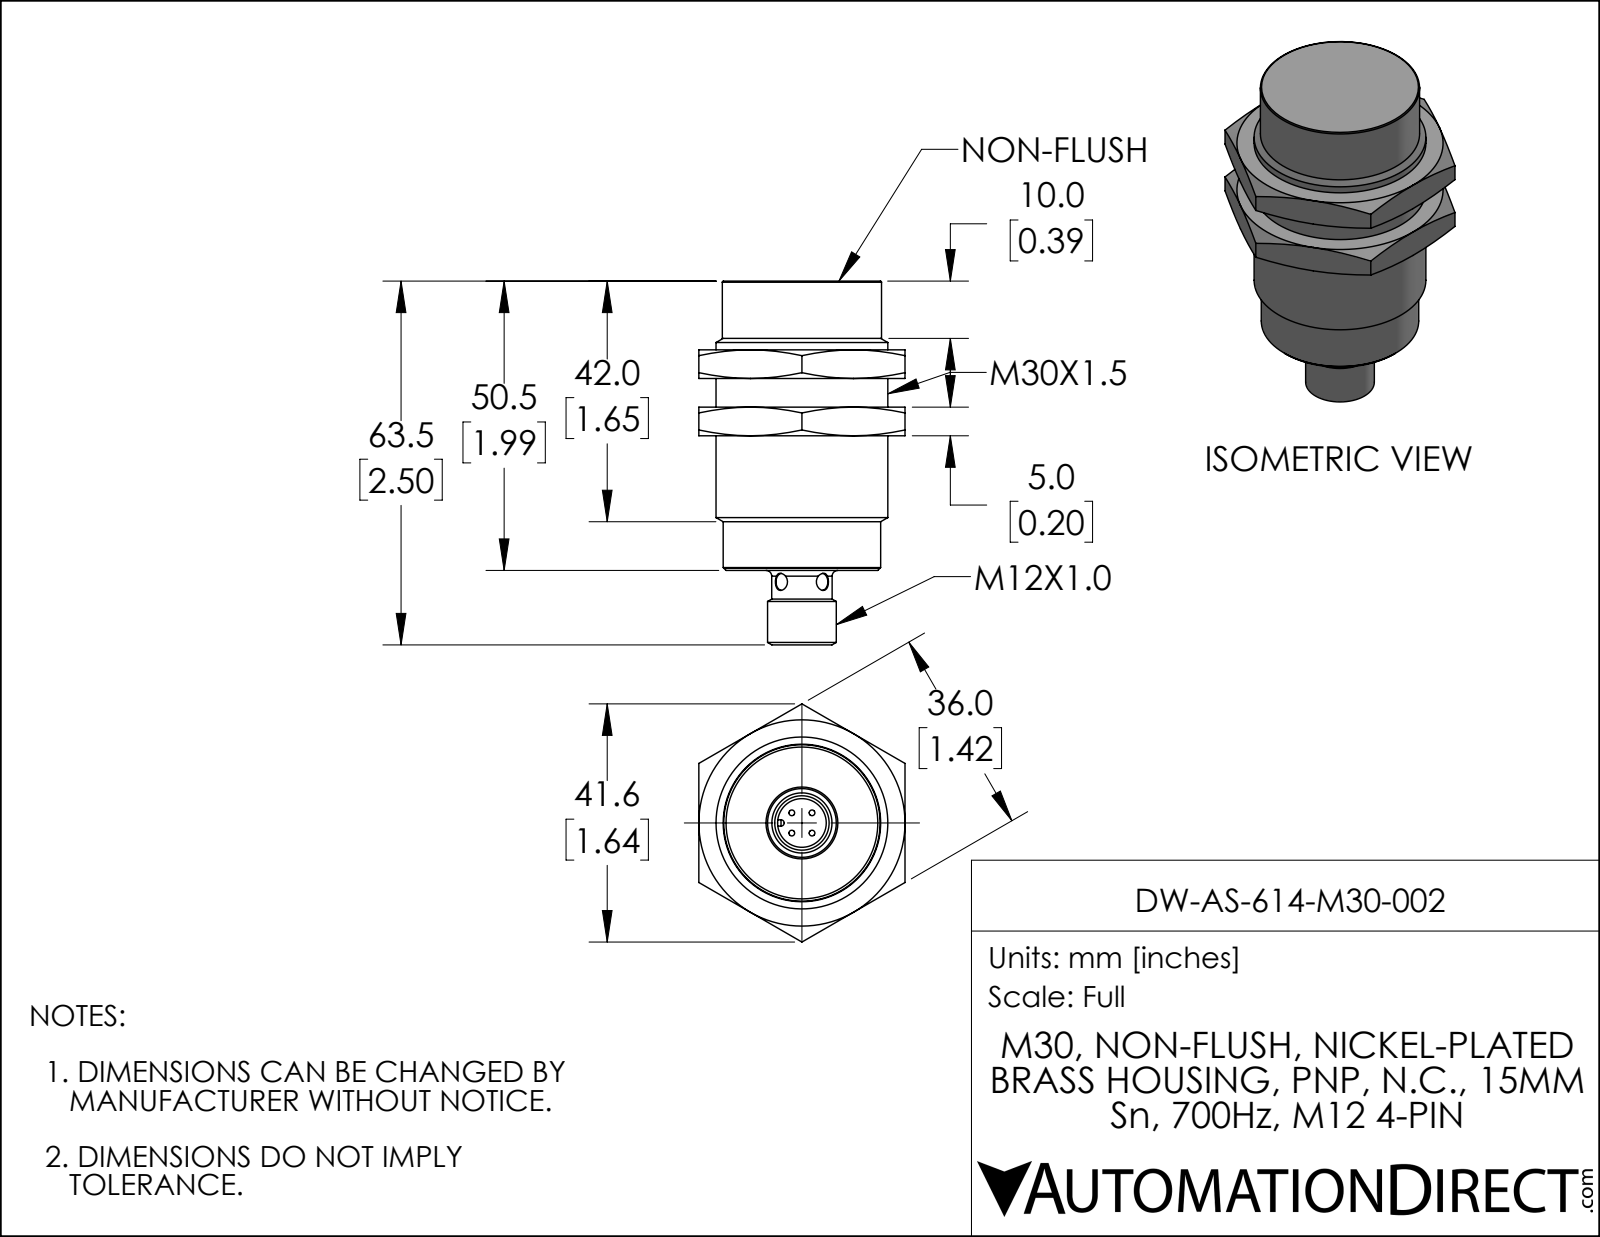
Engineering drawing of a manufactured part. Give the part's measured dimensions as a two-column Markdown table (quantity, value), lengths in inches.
| quantity | value |
| --- | --- |
| part name | DW-AS-614-M30-002 |
| STEP written by | SolidWorks 2019 (AUTOMOTIVE_DESIGN) |
| units | inches |
| bodies | 1 solid, 84 faces (28 planar, 19 cylindrical, 37 other) |
| overall size | 2.5 × 1.637 × 1.417 |
| volume | 2.351 in³ |
| surface area | 13.28 in² |
| round holes (diameter × count) | 0.118 × 2, 0.335 × 1 |
| round bosses / shafts (diameter × count) | 0.039 × 4, 1.181 × 1, 1.094 × 1, 1.083 × 1, 1.075 × 1, 0.472 × 1, 0.415 × 1 |
| partial cylindrical surfaces (radius × count) | 0.022 × 2 |
| main face-to-face distances | 0.197, 0.394, 1.417, 1.988, 0.472, 0.669, 1.516, 0.866, 1.122, 1.063 |
